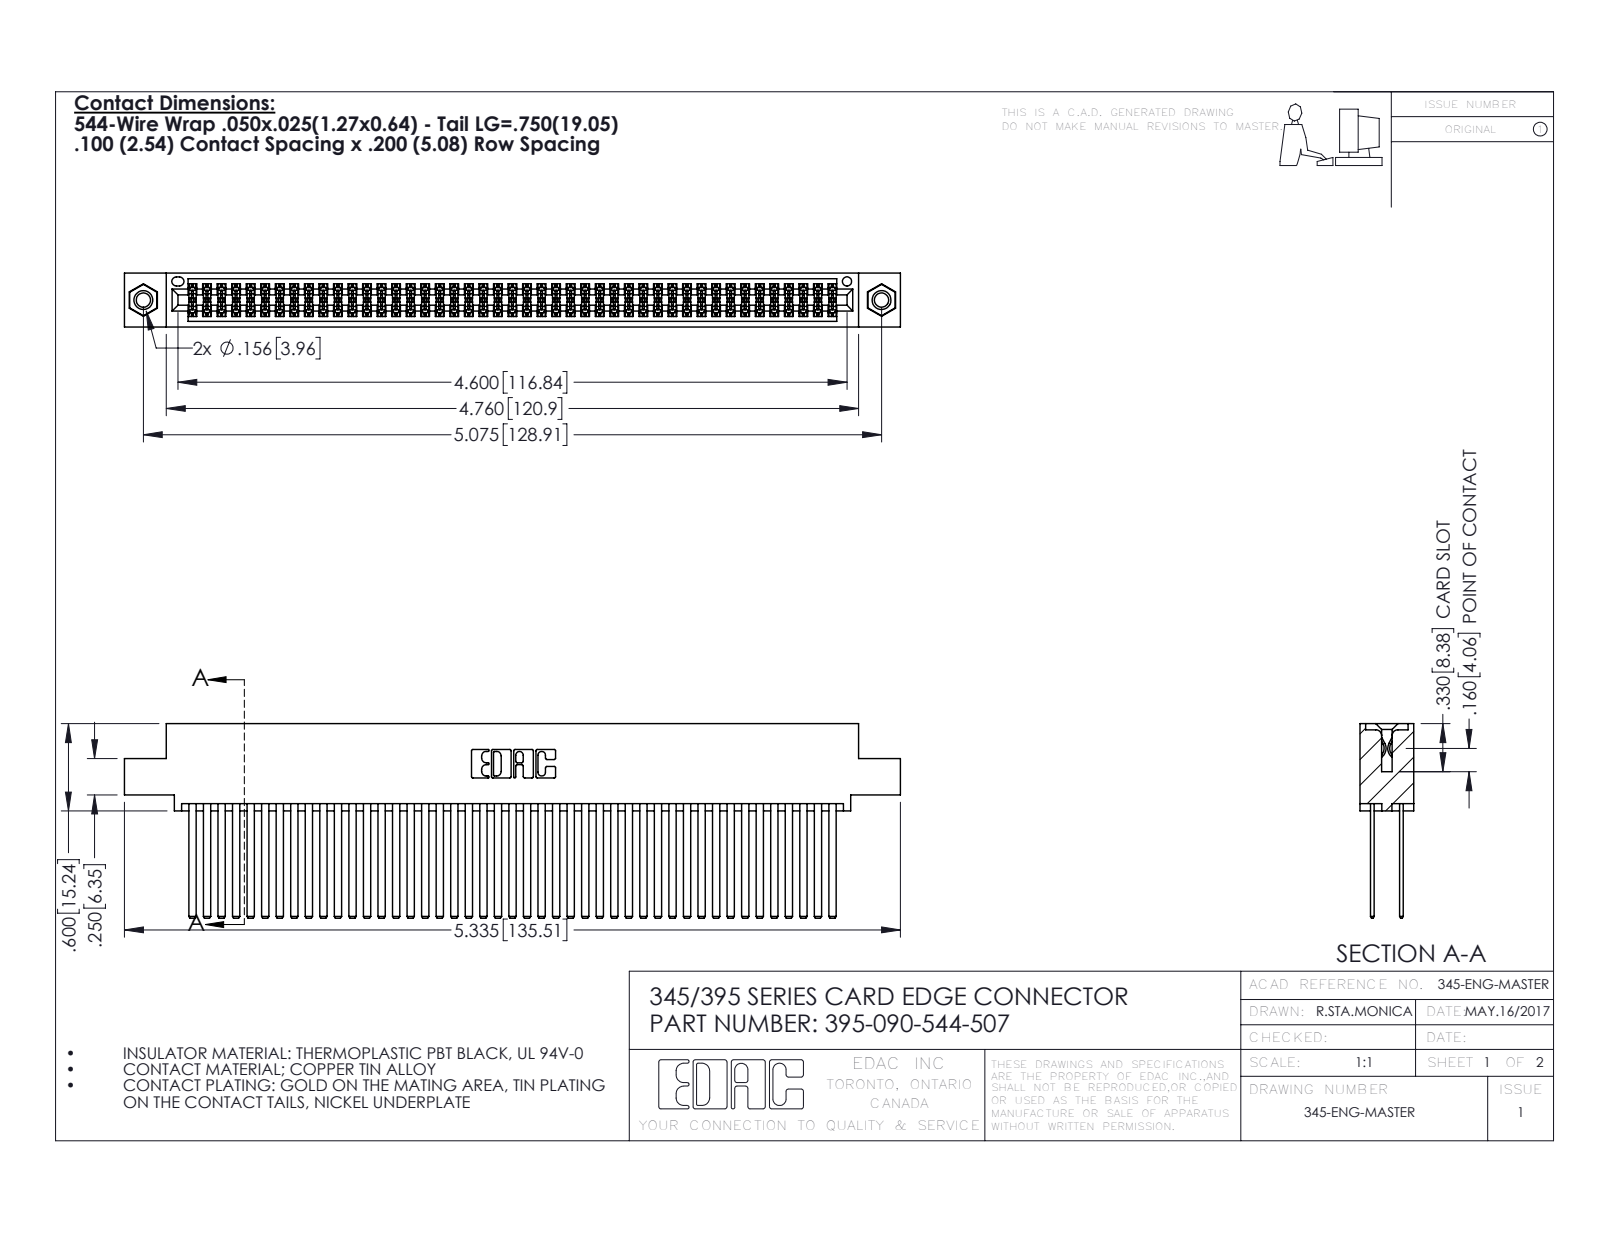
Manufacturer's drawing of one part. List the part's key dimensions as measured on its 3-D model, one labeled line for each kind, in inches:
Part name (STEP PRODUCT): 345-250-001_345-250-005-103; 345 Part_0.110 Offset - 0.156 Dia-TI; 345-292-001_345-293-144; 395-090-544-507
STEP written by: SolidWorks 2016 (CONFIG_CONTROL_DESIGN)
Units: inches
Bodies: 93 solids, 4150 faces (2726 planar, 1408 cylindrical, 16 other)
Overall size (bounding box): 5.335 × 1.337 × 0.37
Volume: 0.877 in³ · Surface area: 38.92 in²
Round holes (diameter × count): ⌀0.098 ×2, ⌀0.125 ×2, ⌀0.156 ×2, ⌀0.064 ×1
Round bosses / shafts (diameter × count): ⌀0.155 ×2
Partial cylindrical surfaces — rounded edges, fillets, slot ends (radius × count): R0.006 ×135, R0.01 ×22, R0.007 ×6, R0.031 ×6, R0.026 ×3, R0.014 ×2, R0.019 ×2, R0.022 ×2
Main face-to-face distances: 0.2, 0.025, 0.072, 0.098, 0.272, 0.298, 0.225, 0.175, 0.37, 0.05
Hole centre spacings: 0.27, 4.839, 5.075
